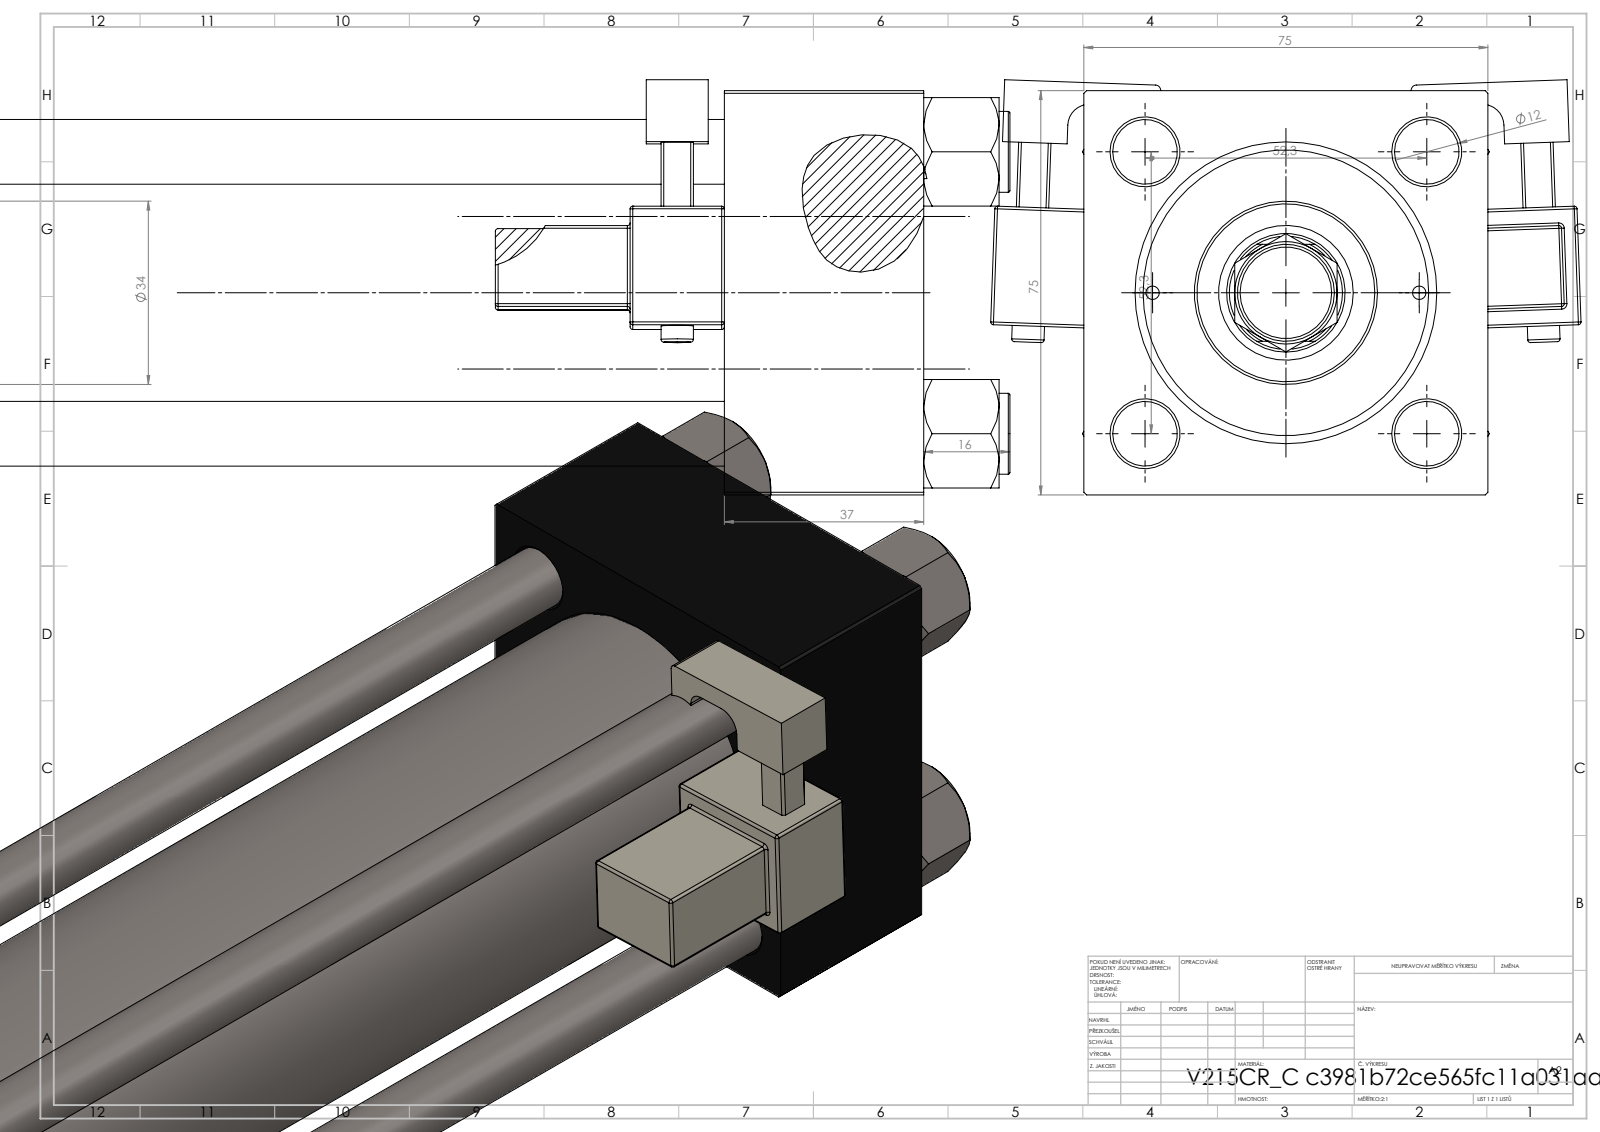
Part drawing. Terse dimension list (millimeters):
name: MFA; V215CR_C_Body; V215CR_VCP_C; NUT_M5_C (+3 more)
written by: SolidWorks 2019 (CONFIG_CONTROL_DESIGN)
unit: mm
bodies: 14 solids, 1360 faces (602 planar, 154 cylindrical, 604 other)
size: 558 × 109.57 × 77.03
volume: 1 146 000 mm³; area: 344 794 mm²
holes: 4× ⌀12, 2× ⌀2.5, 2× ⌀7, 2× ⌀20.96, 2× ⌀30, 1× ⌀10.5, 1× ⌀22, 1× ⌀25, 1× ⌀41, 1× ⌀50, 1× ⌀53
bosses: 4× ⌀15, 2× ⌀6, 1× ⌀56, 1× ⌀34, 1× ⌀18, 1× ⌀11
rounds: 48× R0.5, 2× R1, 2× R2.5, 2× R4, 1× R10.5
face distances: 75, 37, 484, 447, 425, 388, 59, 455.3, 418.3, 30.3
hole spacings: 26.19, 36.98, 52.3, 57.22, 24.75, 73.96, 49.5, 423.5
